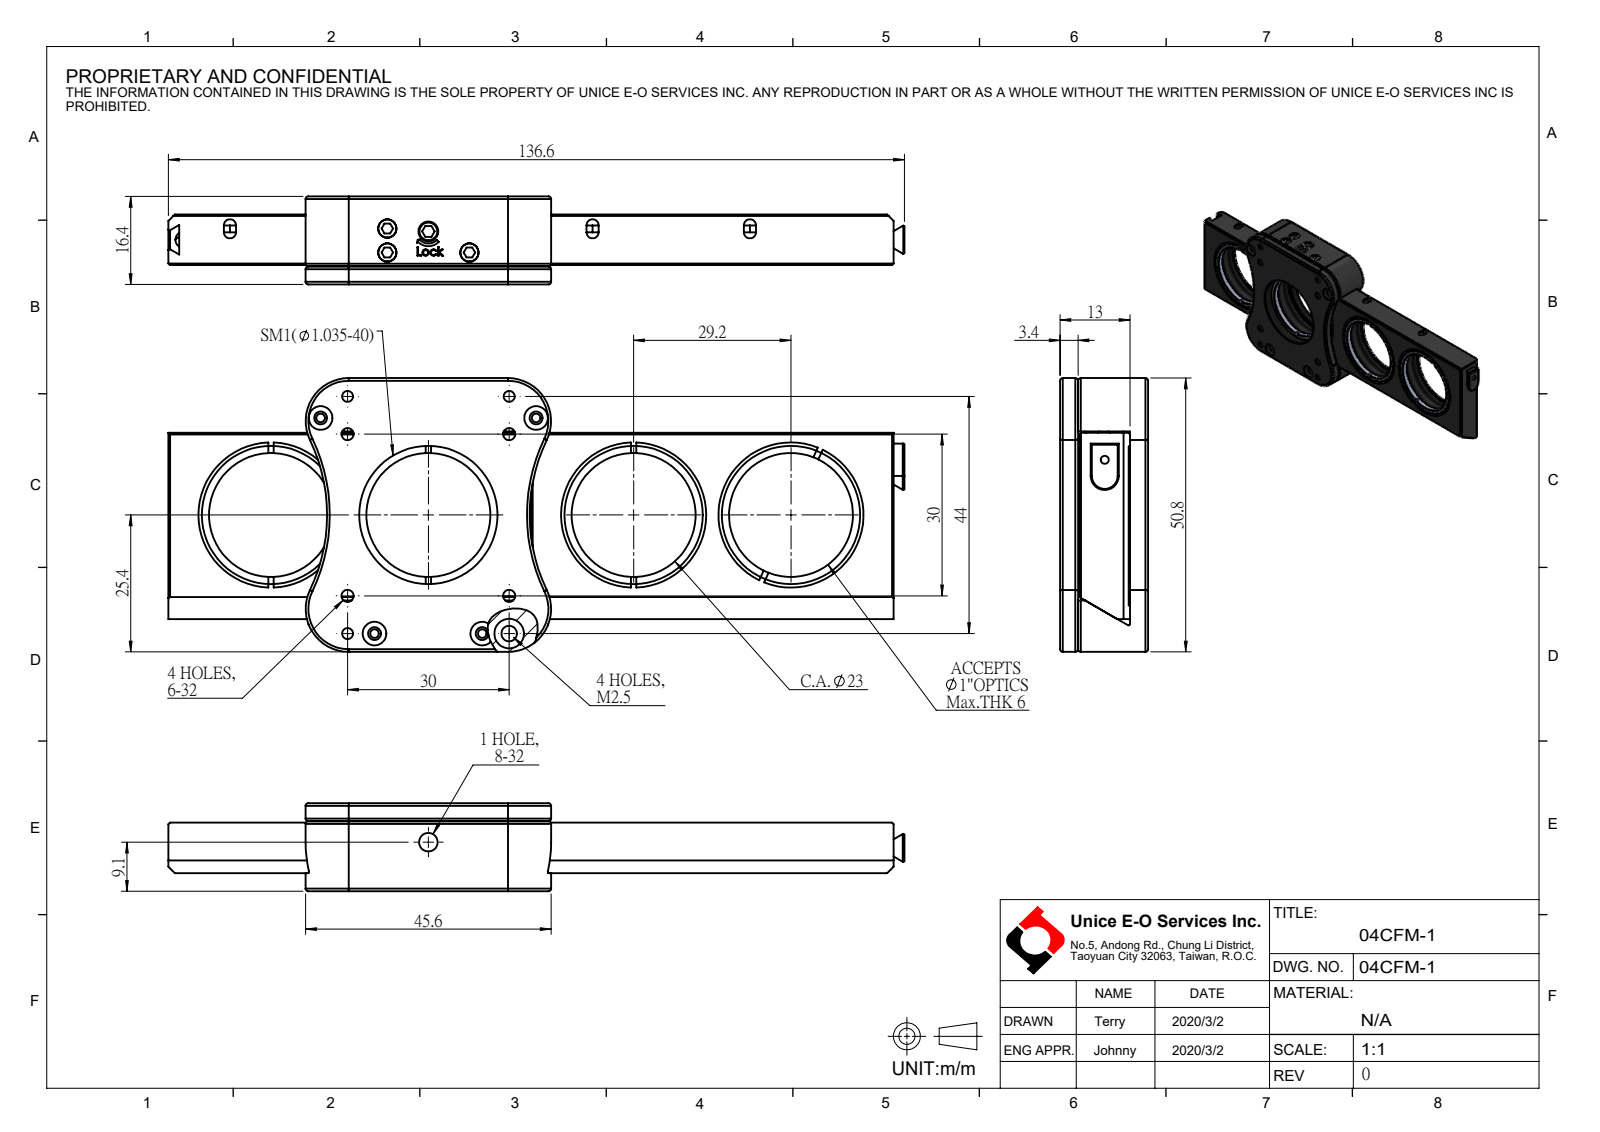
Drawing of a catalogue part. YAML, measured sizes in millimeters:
part_name: "04CFM-1"
step_written_by: "SolidWorks 2016 (CONFIG_CONTROL_DESIGN)"
units: millimeters
bodies: {solids: 0, faces: 314, planar: 135, cylindrical: 115, other: 64}
overall_size: [136.62, 50.8, 16.35]
round_holes:
  - {diameter: 2.05, count: 4}
  - {diameter: 2.26, count: 4}
  - {diameter: 2.4, count: 4}
  - {diameter: 2.9, count: 4}
  - {diameter: 23, count: 4}
  - {diameter: 24, count: 4}
  - {diameter: 25.65, count: 4}
  - {diameter: 3.45, count: 1}
  - {diameter: 4.6, count: 1}
partial_cylinders:
  - {radius: 0.5, count: 8}
  - {radius: 0.2, count: 5}
  - {radius: 8, count: 4}
  - {radius: 32, count: 2}
  - {radius: 0.25, count: 1}
  - {radius: 2.75, count: 1}
  - {radius: 3, count: 1}
face_to_face_distances: [9.4, 3.35, 3.6, 12.75, 13, 9.15, 9.65, 16.35, 2, 2.25]
hole_center_spacings: [30, 7, 21.21, 26.63, 30.81, 37, 47.63, 29.21]
